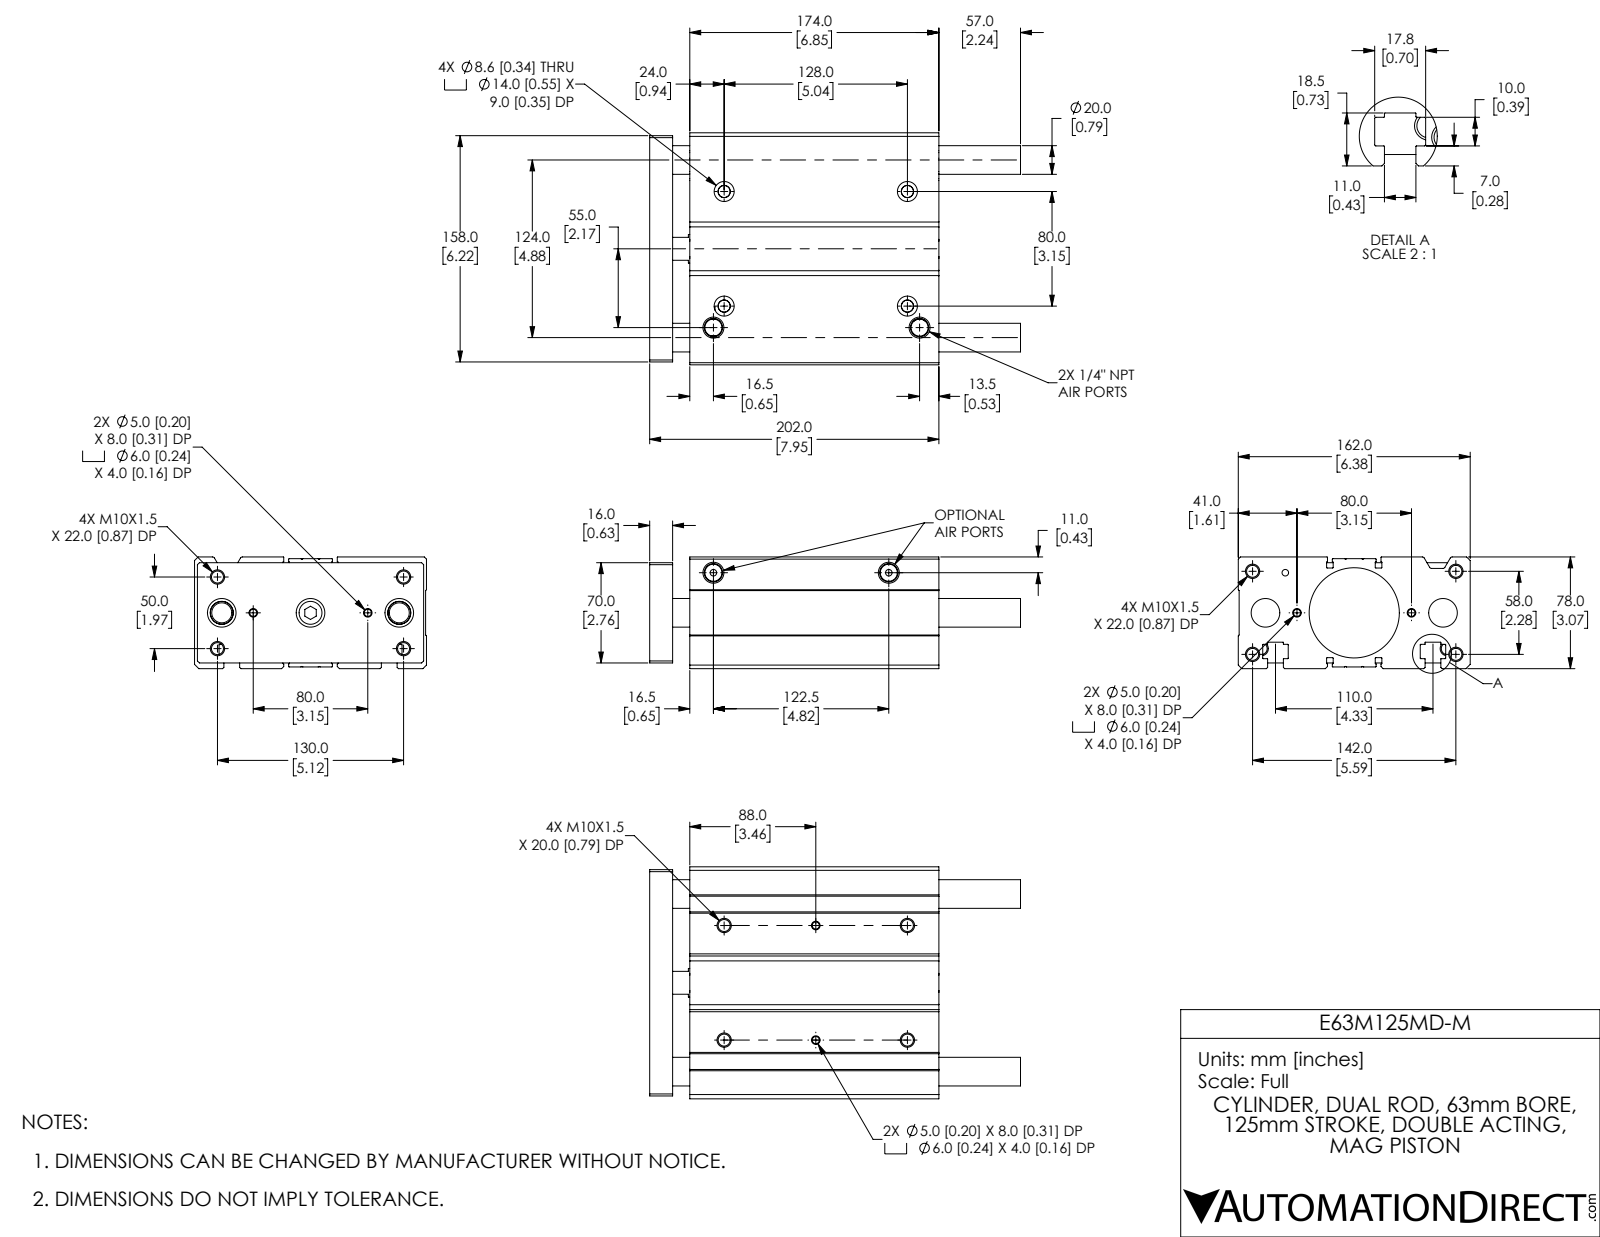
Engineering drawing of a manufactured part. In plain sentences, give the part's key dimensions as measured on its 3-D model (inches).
The part is named "E63M125MD-M_ENDPLATE; E63M125MD-M_BODY; E63M125MD-M". Its 3-D file was written by "SolidWorks 2019 (CONFIG_CONTROL_DESIGN)". It is 5 solids with 421 faces: 139 planar, 190 cylindrical and 92 other. Overall it measures 10.197 by 6.378 by 3.071 inches. Its volume is 114.1 cubic inches and its surface area 461.5 square inches. Round holes: 12 of diameter 0.33, 4 of diameter 0.197, 4 of diameter 0.236, 4 of diameter 0.339, 4 of diameter 0.551, 3 of diameter 0.18, 3 of diameter 0.394, 3 of diameter 0.787, 2 of diameter 0.63, 1 of diameter 0.787, 1 of diameter 2.48, 1 of diameter 2.48. Round bosses or shafts: 1 of diameter 0.63. Partial cylindrical surfaces (rounded edges, fillets, slot ends): 32 of radius 0.008, 28 of radius 0.016, 4 of radius 0.059, 2 of radius 0.012. The main face-to-face distances are 3.071, 1.102, 0.63, 0.472, 0.047, 3.024, 0.157, 7.953, 7.323, 6.85. The hole center spacings are 0.284, 0.991, 1.195, 1.392, 1.671, 2.139, 2.52, 2.742.
